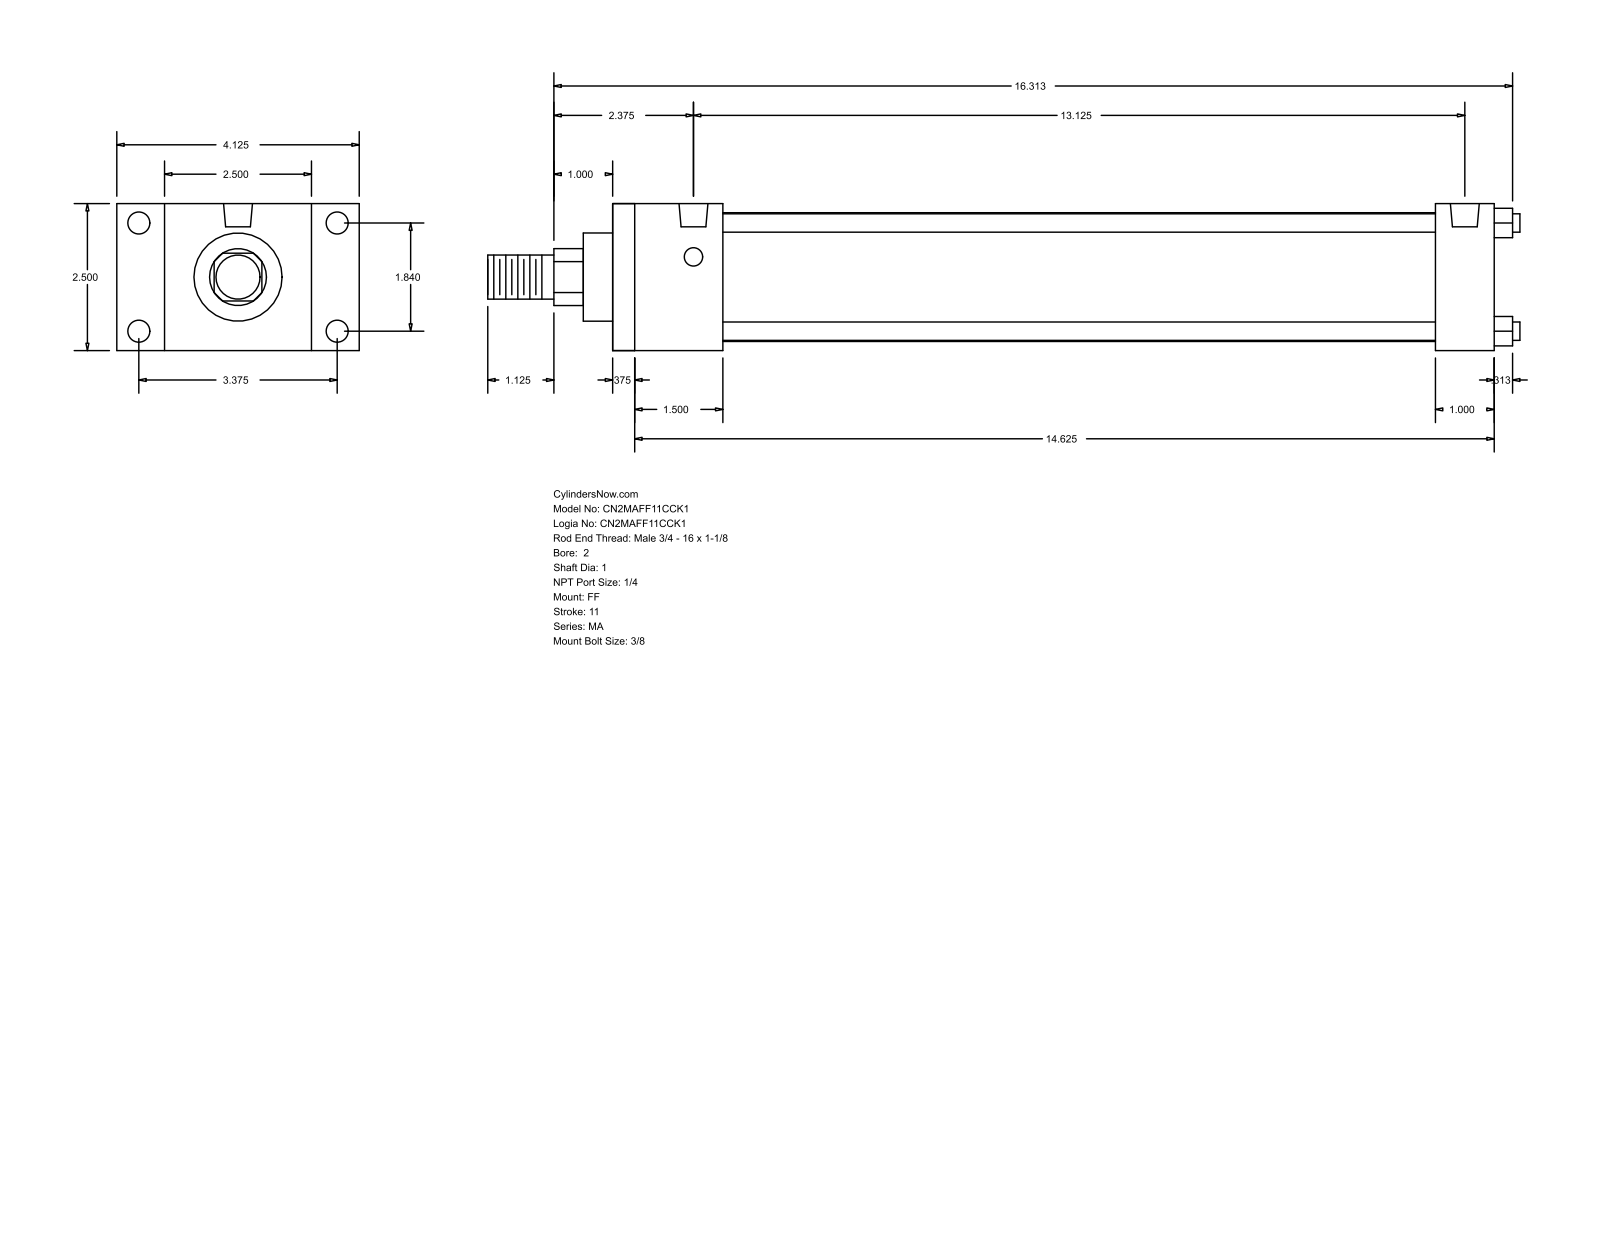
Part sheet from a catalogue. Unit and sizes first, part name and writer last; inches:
Units: inches
Overall size (bounding box): 17.563 × 4.125 × 2.5
Round holes (diameter × count): ⌀0.313 ×4, ⌀0.375 ×4, ⌀0.492 ×2
Round bosses / shafts (diameter × count): ⌀0.313 ×4, ⌀2.19 ×1, ⌀1.5 ×1, ⌀1 ×1, ⌀0.75 ×1
Partial cylindrical surfaces — rounded edges, fillets, slot ends (radius × count): R0.484 ×1
Main face-to-face distances: 2.5, 15, 0.375, 14.625, 1, 0.813, 0.5, 1.875, 14, 1.5
Hole centre spacings: 1.84, 3.375, 3.844, 13.125
Bodies: 0 solids, 92 faces (64 planar, 28 cylindrical, 0 other)
Part name (STEP PRODUCT): MA_FF__0200_1
STEP written by: GSSL Pune (CONFIG_CONTROL_DESIGN)
